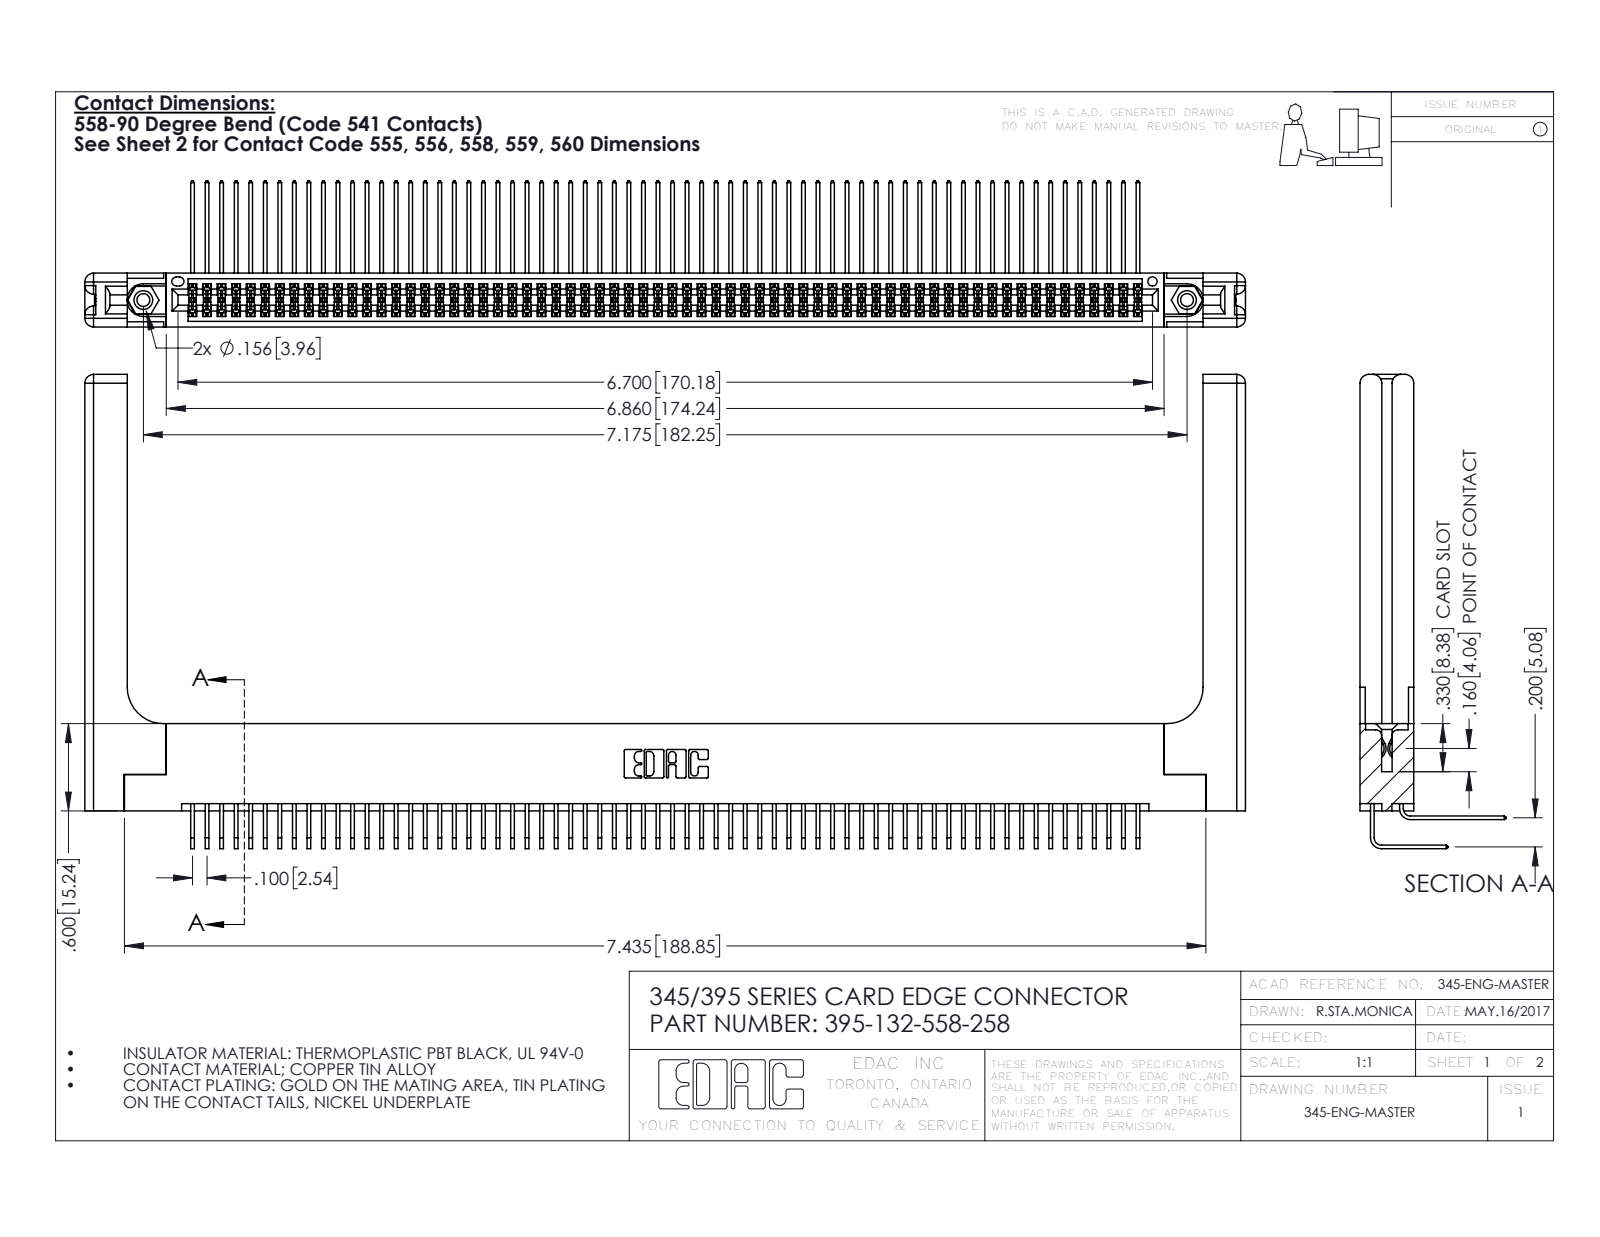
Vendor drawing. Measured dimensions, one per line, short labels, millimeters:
name: 345 Part_Flush Mounting Lugs - 0.156 Dia-TH; 345-220-058_345-220-058; 345-292-001_558 Tail - 2; 395-132-558-258 (+2 more)
written by: SolidWorks 2016 (CONFIG_CONTROL_DESIGN)
unit: mm
bodies: 137 solids, 7246 faces (4848 planar, 2338 cylindrical, 60 other)
size: 202.7 × 82.8 × 25.5
volume: 29 150 mm³; area: 39 660 mm²
holes: 2× ⌀2.3, 2× ⌀3.2, 2× ⌀4, 1× ⌀1.6
bosses: 2× ⌀3.9
rounds: 199× R0.2, 22× R0.3, 16× R1.5, 6× R0.2, 6× R0.8, 3× R0.7, 2× R0.4, 2× R0.5
face distances: 1.8, 7.6, 5.1, 9.4, 2.5, 6.9, 0.6, 5.7, 0.6, 7.2
hole spacings: 6.9, 176.3, 182.2
